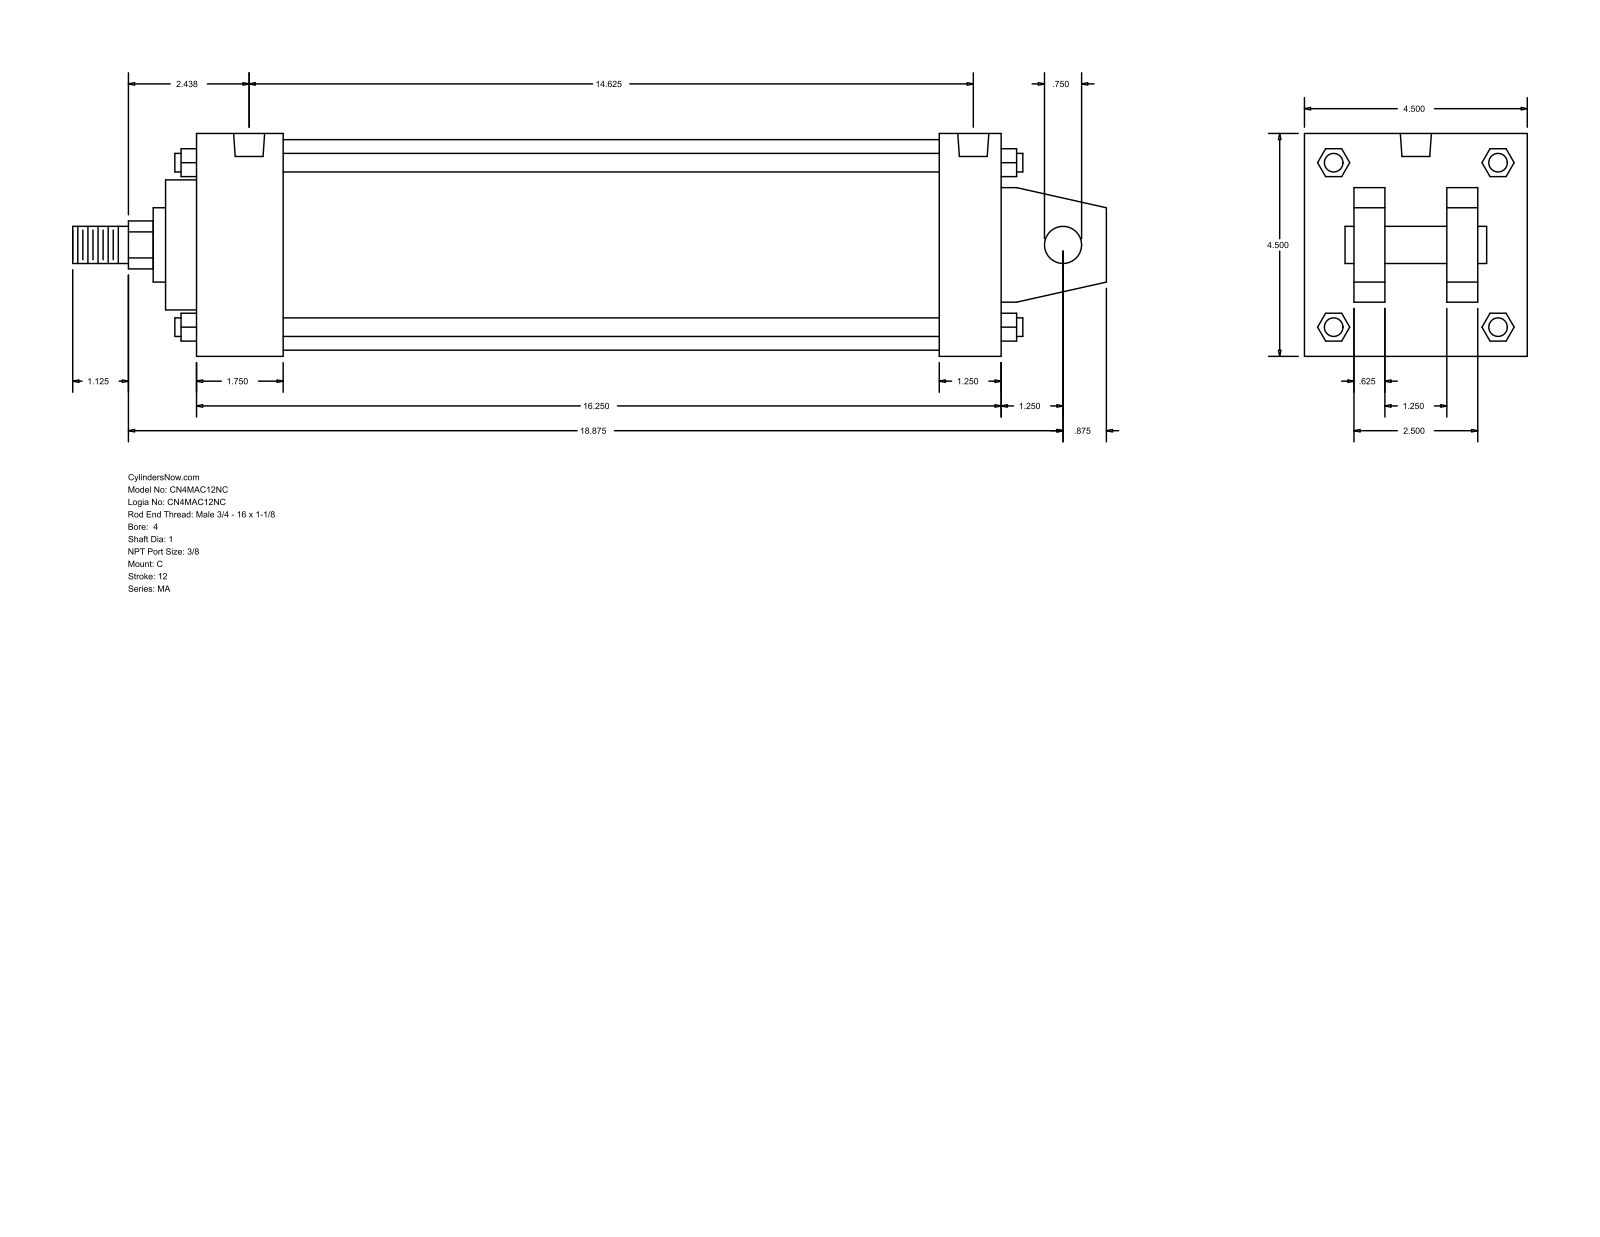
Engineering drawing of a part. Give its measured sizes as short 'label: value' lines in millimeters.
name: MA_C__0400_1
written by: GSSL Pune (CONFIG_CONTROL_DESIGN)
unit: mm
bodies: 0 solids, 141 faces (109 planar, 32 cylindrical, 0 other)
size: 530.23 × 114.3 × 114.3
holes: 4× ⌀11.11, 2× ⌀15.93
bosses: 4× ⌀9.53, 2× ⌀19.05, 1× ⌀107.95, 1× ⌀66.67, 1× ⌀38.1, 1× ⌀25.4
rounds: 1× R12.29
face distances: 114.3, 412.76, 15.87, 73.03, 41.27, 25.4, 88.9, 47.63, 381.01, 31.75
hole spacings: 361.95, 4.76, 4.77, 366.71, 366.72, 371.48
